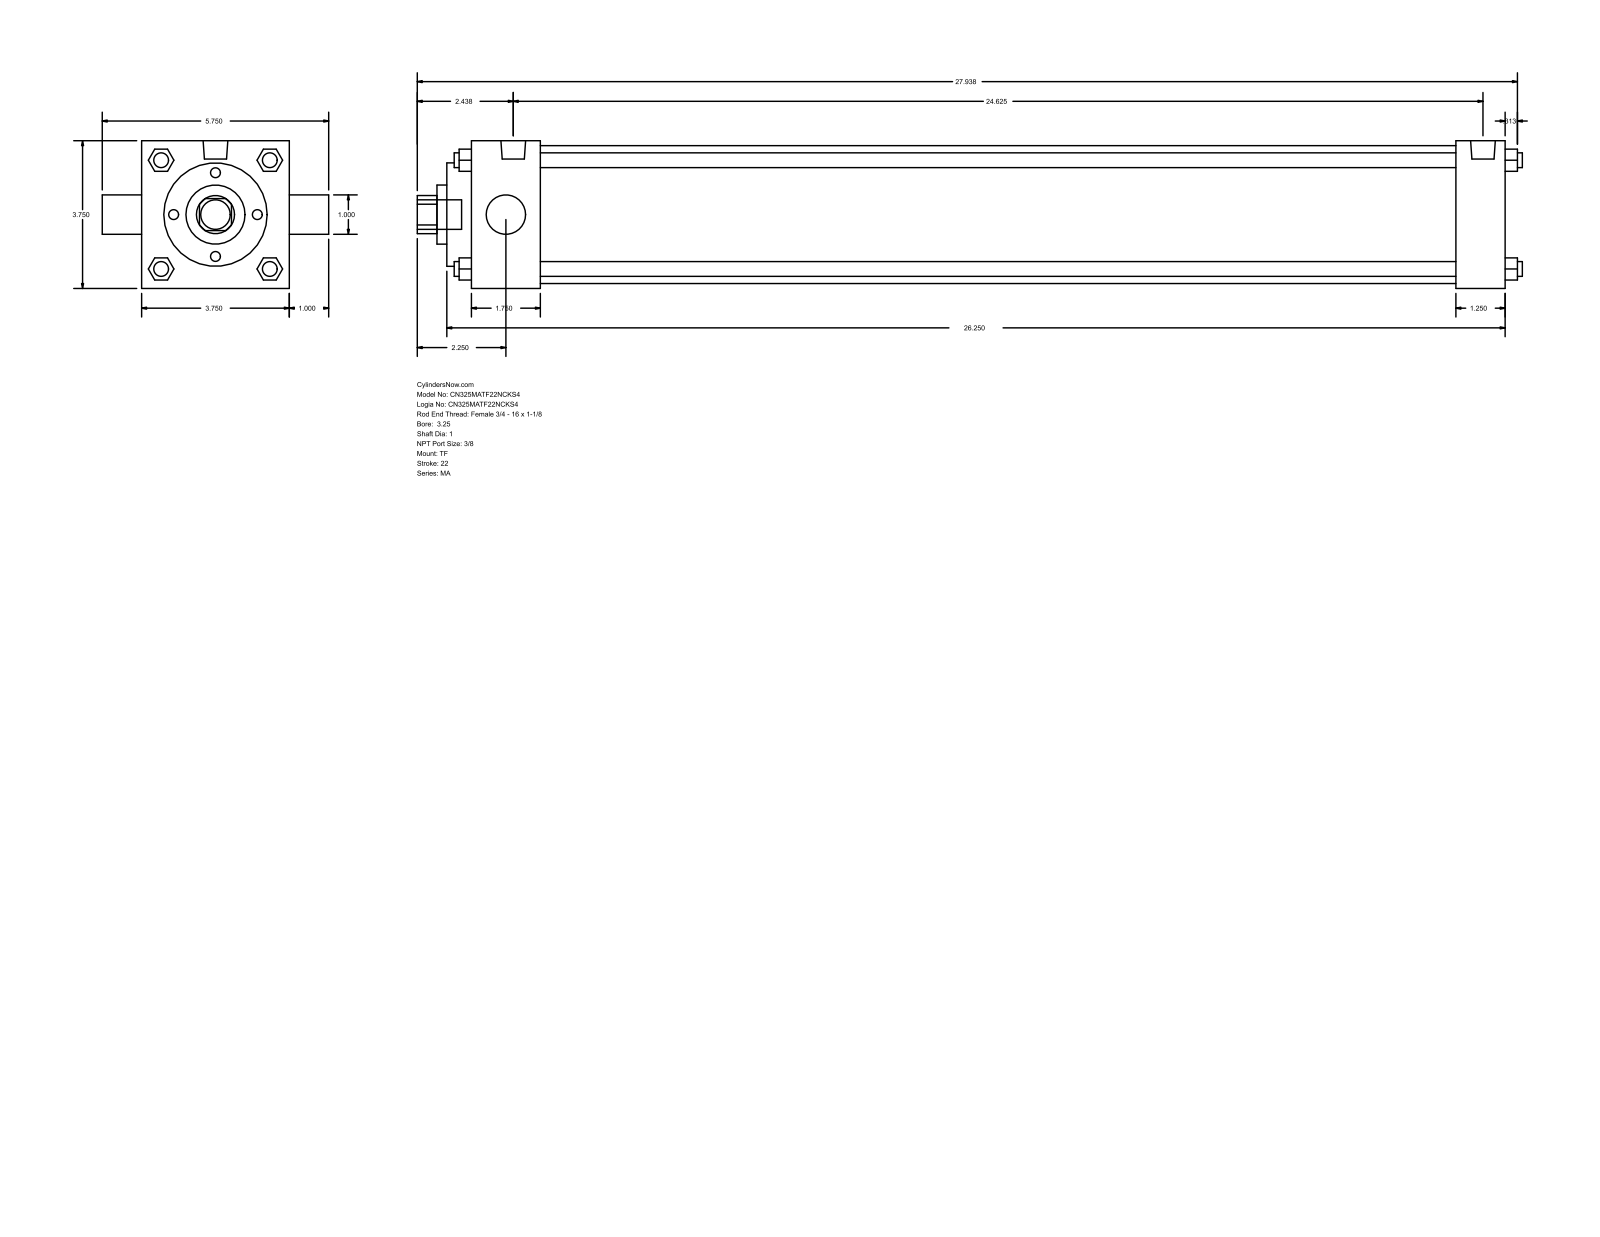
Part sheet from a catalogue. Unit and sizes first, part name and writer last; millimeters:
Units: millimetres
Overall size (bounding box): 712.79 × 146.05 × 95.25
Round holes (diameter × count): ⌀25.4 ×2, ⌀38.1 ×1, ⌀66.67 ×1, ⌀88.9 ×1
Round bosses / shafts (diameter × count): ⌀9.53 ×4, ⌀11.11 ×3, ⌀15.93 ×2, ⌀19.05 ×1
Partial cylindrical surfaces — rounded edges, fillets, slot ends (radius × count): R12.29 ×1
Main face-to-face distances: 95.24, 666.75, 682.62, 15.87, 44.46, 635, 590.54, 622.29, 31.75, 60.33
Bodies: 0 solids, 122 faces (93 planar, 29 cylindrical, 0 other)
Part name (STEP PRODUCT): MA_TF__0325_1
STEP written by: GSSL Pune (CONFIG_CONTROL_DESIGN)
